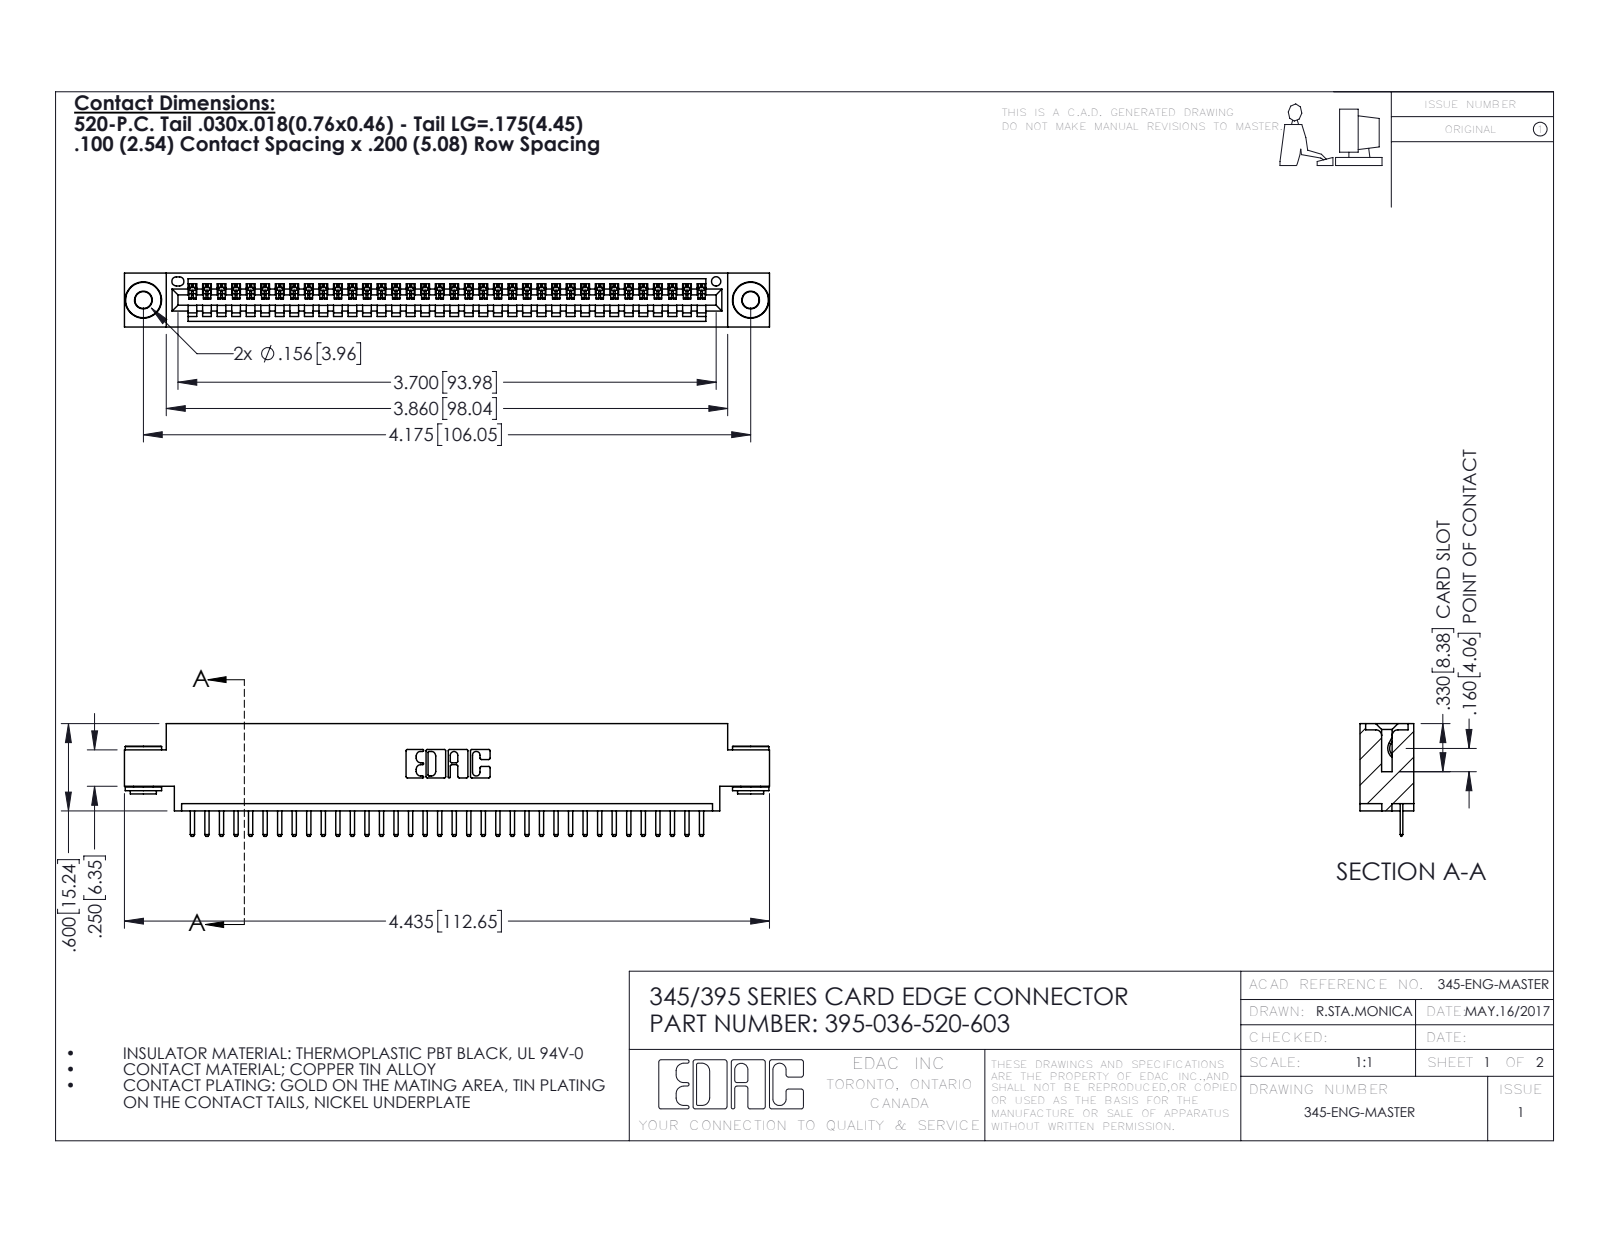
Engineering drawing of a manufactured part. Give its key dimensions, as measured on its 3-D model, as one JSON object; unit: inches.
{"part_name": "395-036-520-603; 345-250-002_345-250-002-102; 345 Part_0.170 Offset - 0.156 Dia-TH; 345-292-001_345-293-120", "step_written_by": "SolidWorks 2016 (CONFIG_CONTROL_DESIGN)", "units": "inches", "bodies": {"solids": 39, "faces": 2400, "planar": 1606, "cylindrical": 786, "other": 8}, "overall_size": [4.435, 0.775, 0.37], "volume_in3": 0.638, "surface_area_in2": 21.41, "round_holes": [[0.116, 2], [0.156, 2], [0.064, 1]], "round_bosses_or_shafts": [[0.25, 2], [0.18, 2], [0.136, 2]], "partial_cylinders_radius": [[0.01, 74], [0.006, 72], [0.01, 22], [0.007, 6], [0.031, 6], [0.026, 3], [0.031, 2], [0.04, 2]], "face_to_face_distances": [0.072, 0.298, 0.37, 0.2, 0.098, 0.272, 0.025, 0.225, 0.175, 0.072], "hole_center_spacings": [0.27, 3.939, 4.175]}
